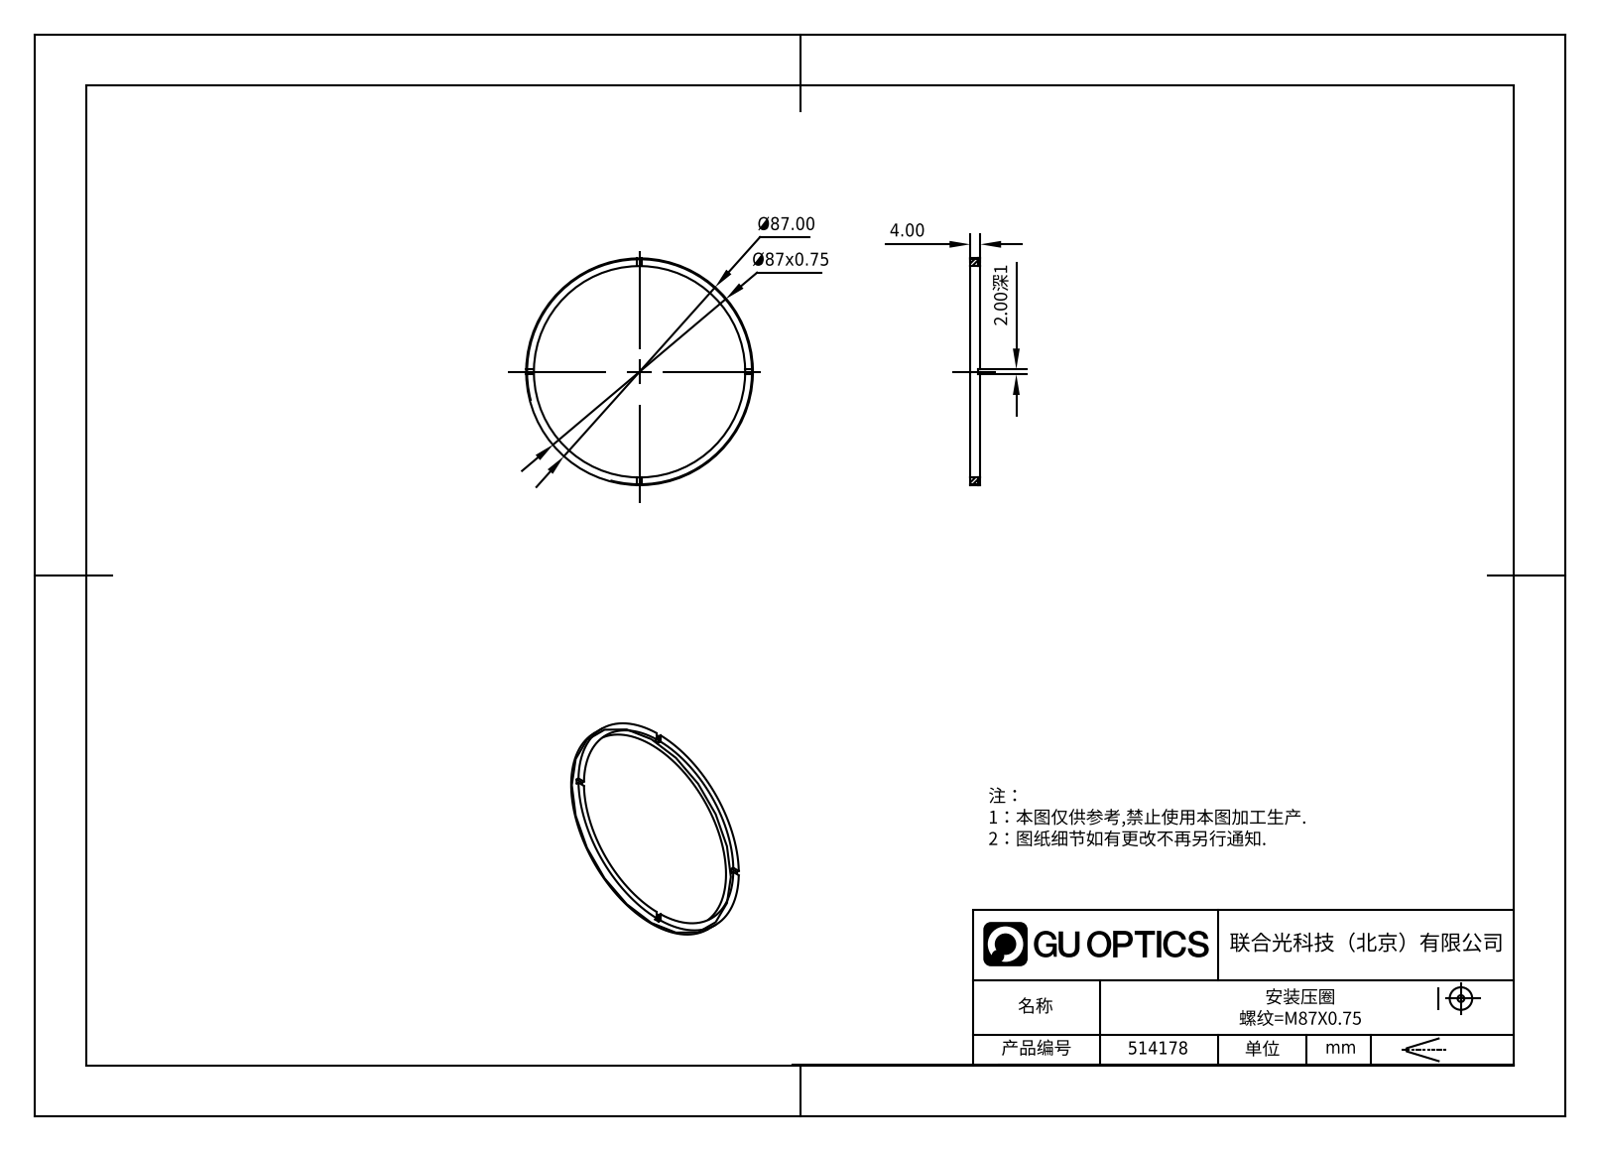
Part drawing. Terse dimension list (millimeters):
name: 514178
written by: SolidWorks 2020 (CONFIG_CONTROL_DESIGN)
unit: mm
bodies: 1 solid, 21 faces (17 planar, 4 cylindrical, 0 other)
size: 87 × 87 × 4
volume: 3 143 mm³; area: 3 703 mm²
holes: 1× ⌀81
bosses: 1× ⌀87
face distances: 4, 3, 1, 2
